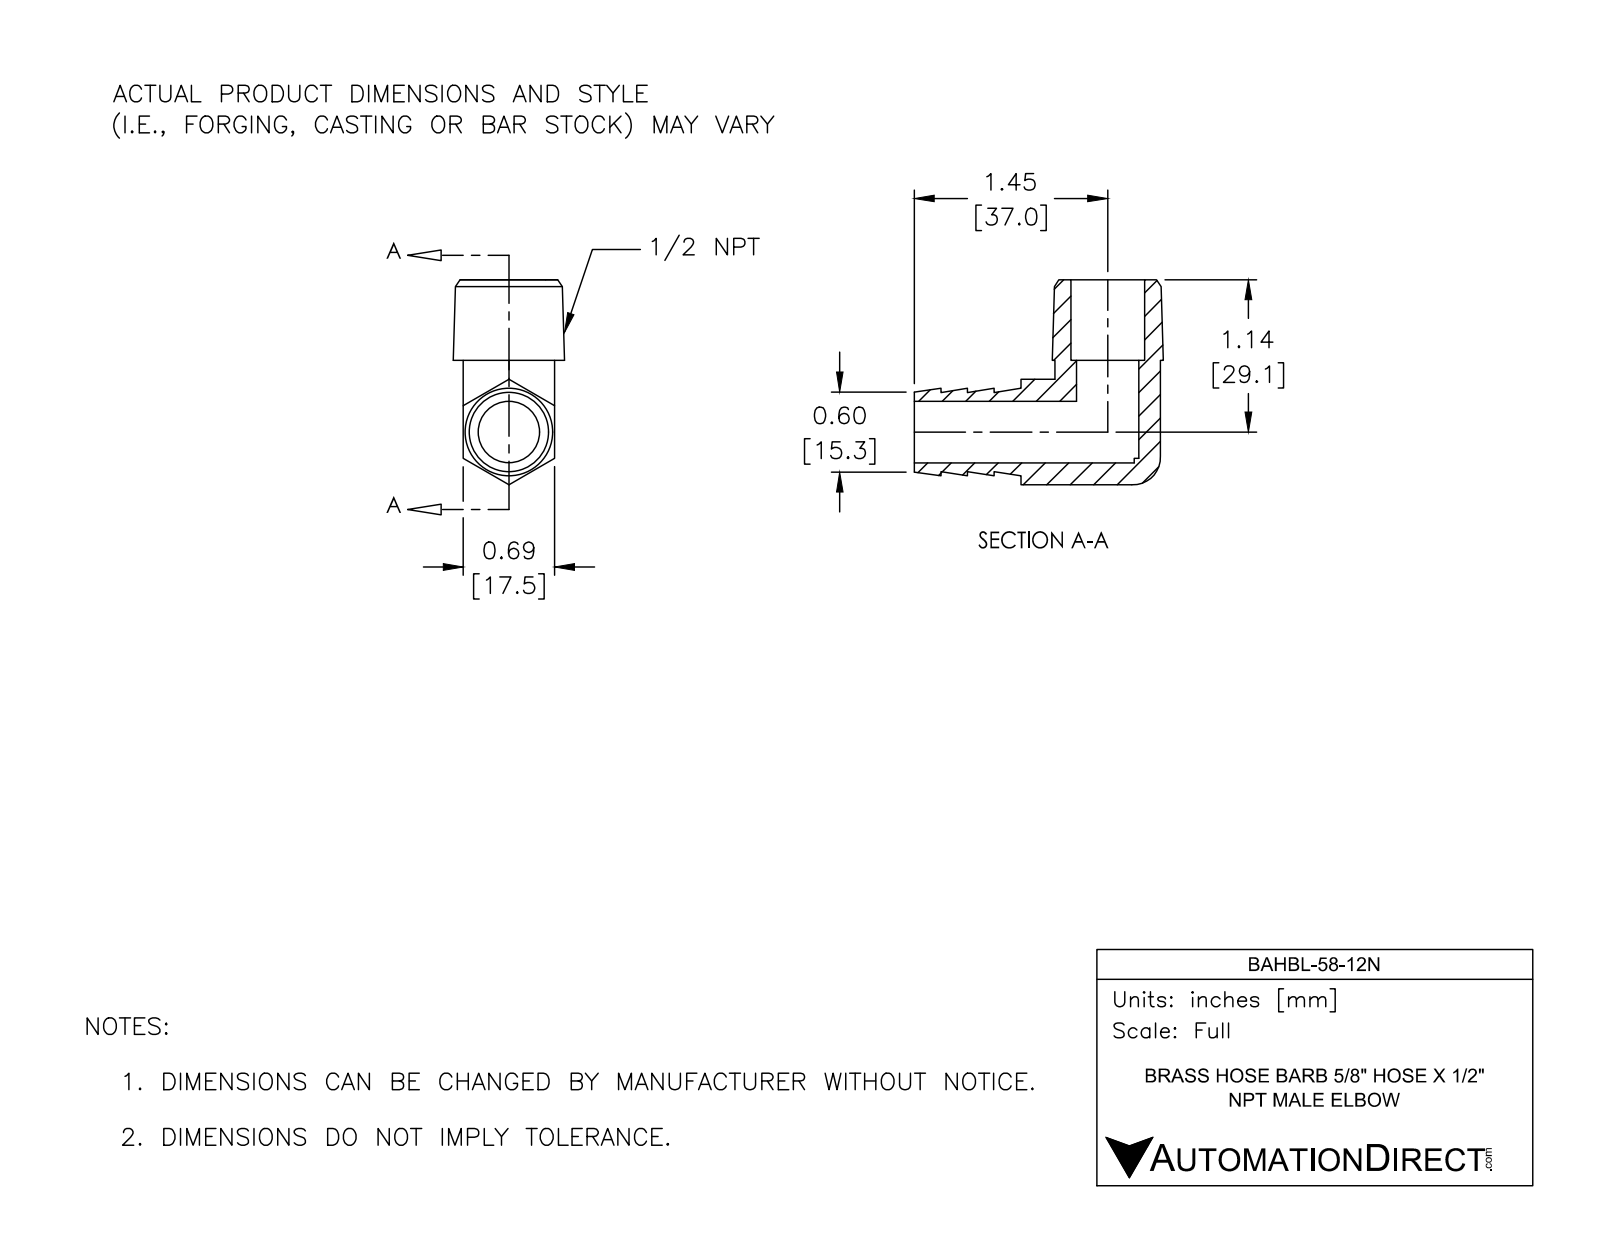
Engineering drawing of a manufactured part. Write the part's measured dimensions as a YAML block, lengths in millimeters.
part_name: "BAHBL-58-12N"
step_written_by: "SolidWorks 2017 (AUTOMOTIVE_DESIGN)"
units: millimeters
bodies: {solids: 1, faces: 47, planar: 22, cylindrical: 13, other: 12}
overall_size: [47.6, 39.2, 21.2]
volume: 9110
surface_area: 6929
round_holes:
  - {diameter: 11.8, count: 1}
  - {diameter: 11.9, count: 1}
  - {diameter: 14.1, count: 1}
round_bosses_or_shafts:
  - {diameter: 16.7, count: 1}
partial_cylinders:
  - {radius: 6.4, count: 2}
face_to_face_distances: [17.5, 17.5, 5.1, 15.4, 10.2, 18.8, 34.1, 20.4, 21.6, 42]
